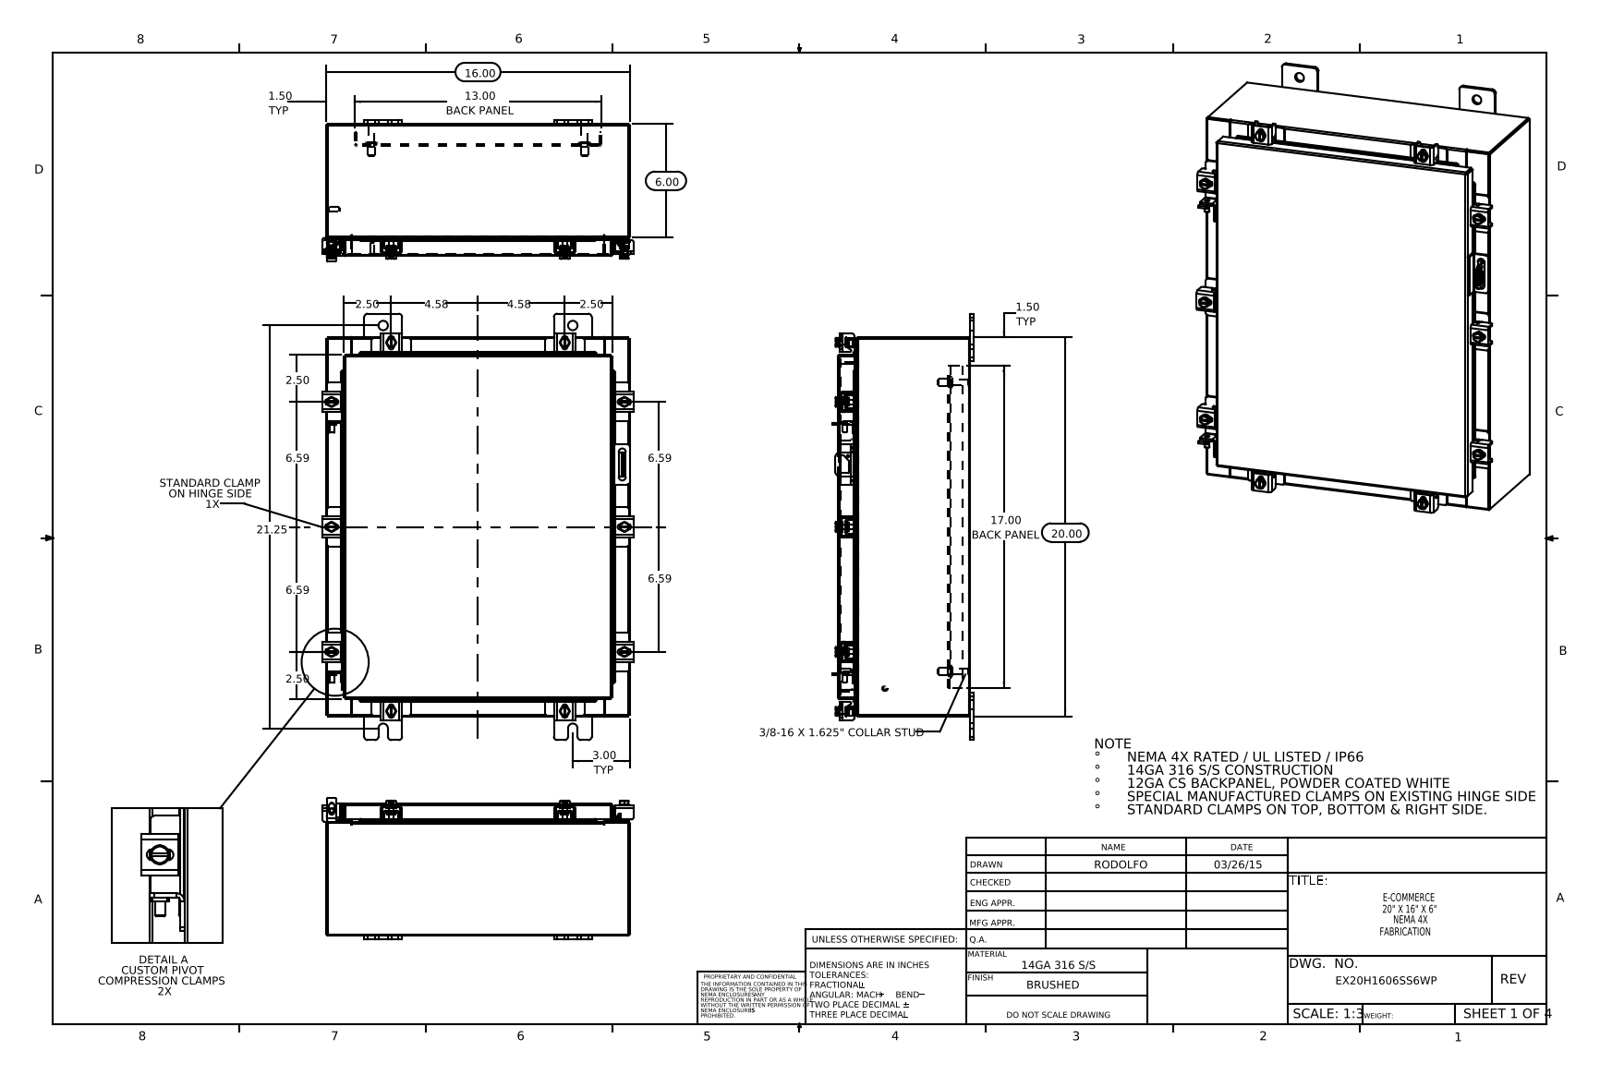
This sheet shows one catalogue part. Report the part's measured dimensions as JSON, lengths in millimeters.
{"part_name": "EX20H1606SS6WP Bottom; EX20H1606SS6WP Standard Clamps; ATEX CLAMP HINGE BRAKET; EX20H1606SS6WP Special Clamp (+8 more)", "step_written_by": "SolidWorks 2014 (CONFIG_CONTROL_DESIGN)", "units": "millimeters", "bodies": {"solids": 71, "faces": 1784, "planar": 955, "cylindrical": 685, "other": 144}, "overall_size": [571.5, 417.1, 189.3], "volume_mm3": 2045000, "surface_area_mm2": 2012000, "round_holes": [[5.4, 10], [6.6, 10], [12.7, 8], [3.2, 1], [6.4, 1]], "round_bosses_or_shafts": [[12.7, 10], [6.4, 10], [10.1, 8], [15.9, 4], [9.5, 4], [8.4, 4], [8, 2], [6, 2]], "partial_cylinders_radius": [[1.5, 46], [0.3, 24], [4.8, 24], [2.2, 22], [3.6, 20], [3, 18], [2.3, 16], [2.5, 16]], "face_to_face_distances": [1.9, 175.3, 177.2, 173.4, 2.6, 404.5, 25.4, 27.3, 148, 149.9], "hole_center_spacings": [59.6, 112.8, 167.5, 259.6, 322.5, 365.1, 398.3, 422.1]}
